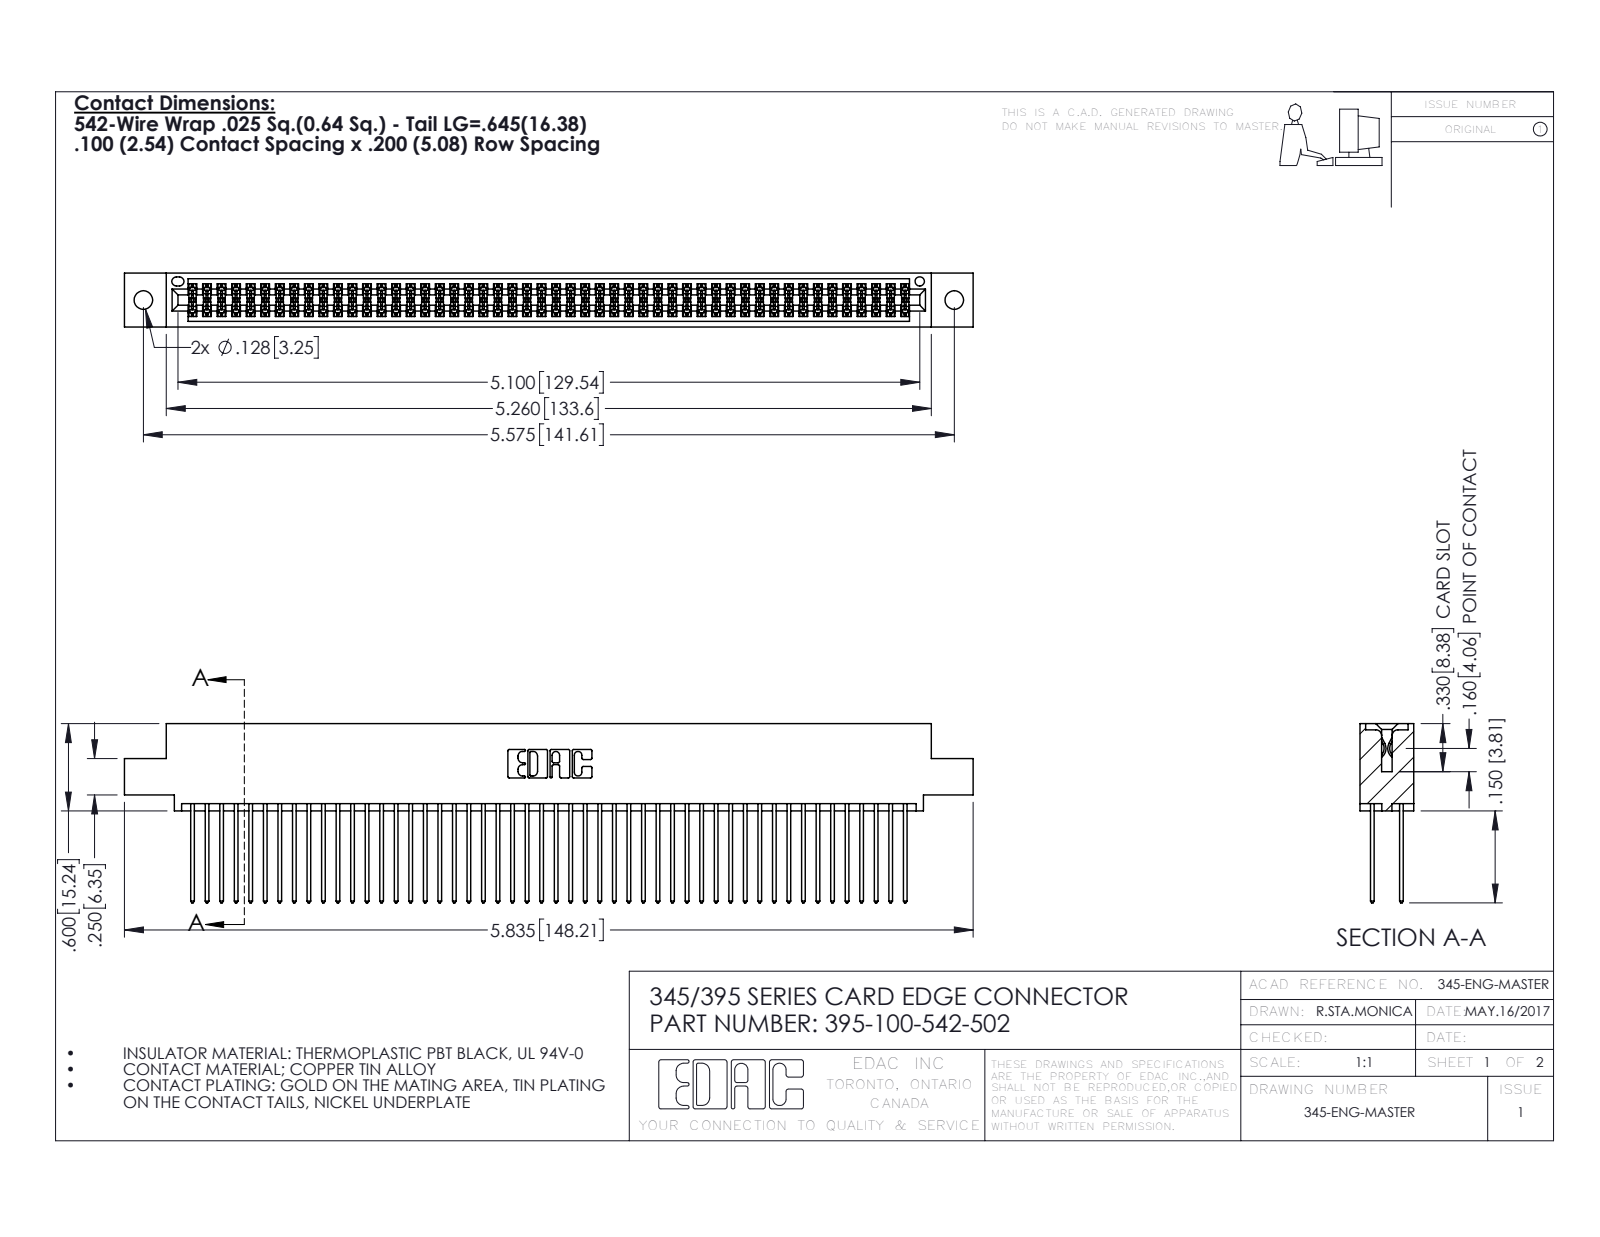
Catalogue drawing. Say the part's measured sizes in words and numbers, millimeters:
The part is named "345-292-001_345-293-142; 395-100-542-502; 345 Part_0.110 Offset - 0.128 Dia". Its 3-D file was written by "SolidWorks 2016 (CONFIG_CONTROL_DESIGN)". It is 101 solids with 5130 faces: 3384 planar, 1746 cylindrical and 0 other. Overall it measures 148.2 by 31.3 by 9.4 millimeters. Its volume is 14 800 cubic millimeters and its surface area 24 070 square millimeters. Round holes: 2 of diameter 3.3, 1 of diameter 1.6. Partial cylindrical surfaces (rounded edges, fillets, slot ends): 150 of radius 0.2, 100 of radius 0.3, 22 of radius 0.3, 6 of radius 0.2, 6 of radius 0.8, 3 of radius 0.7, 2 of radius 0.4, 2 of radius 0.5. The main face-to-face distances are 1.8, 7.6, 5.1, 2.5, 6.9, 0.6, 5.7, 9.4, 4.4, 3.8. The hole center spacings are 6.9, 135.6, 141.6.
